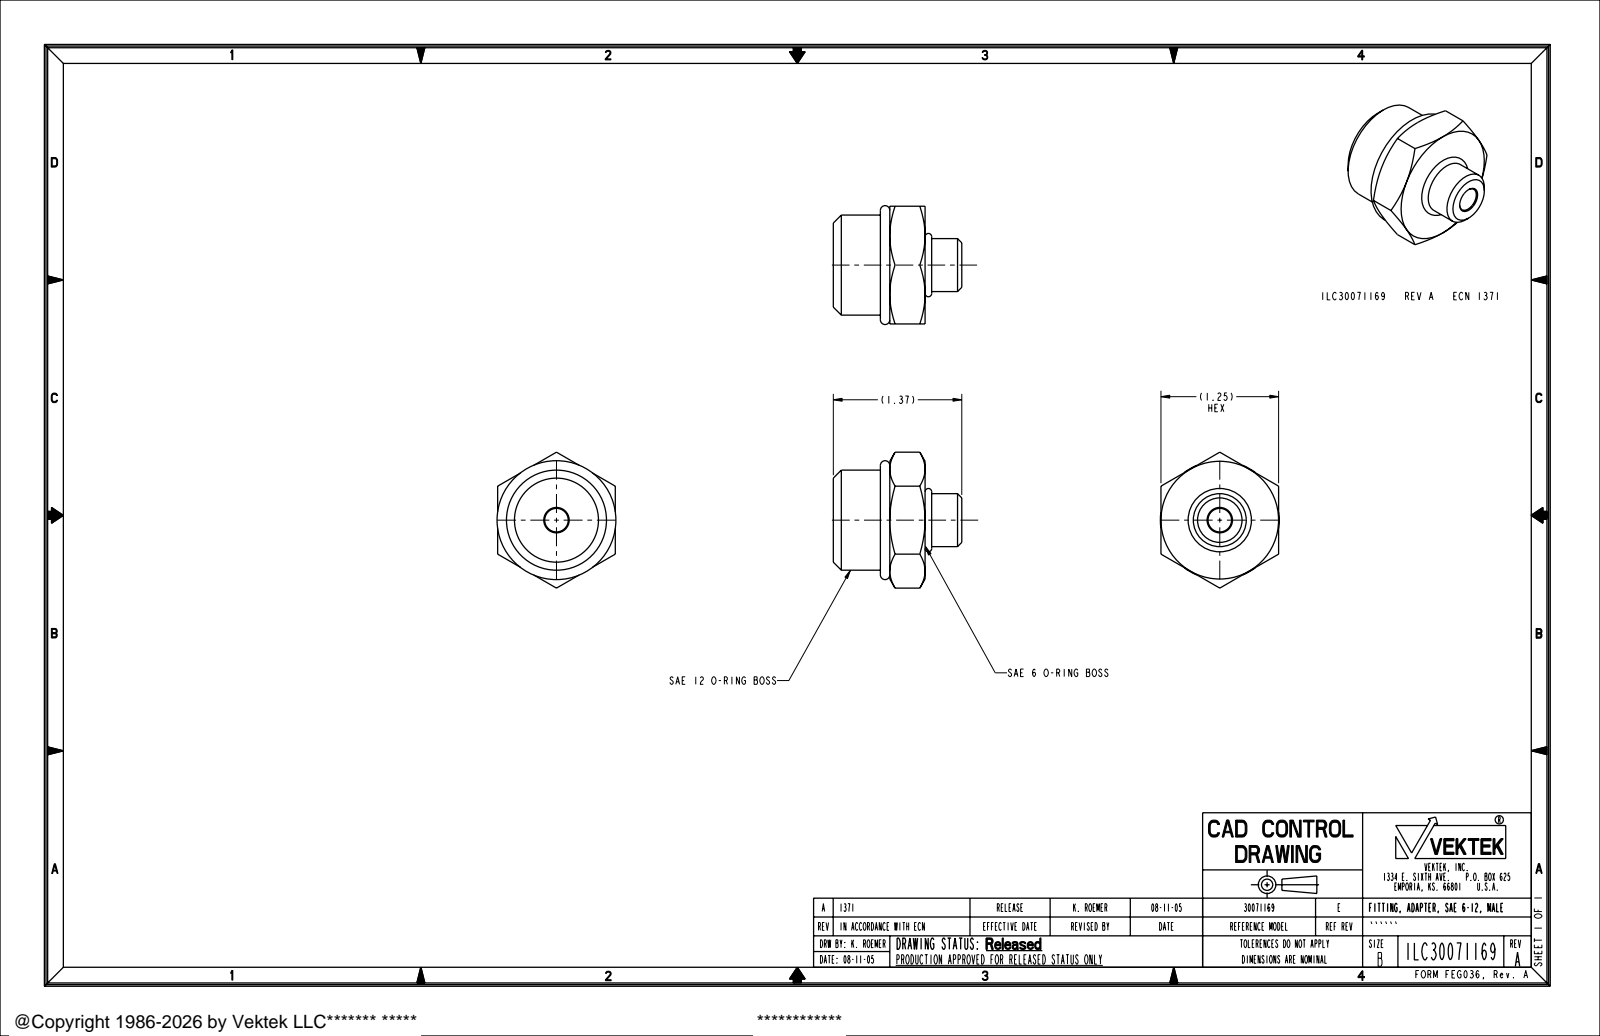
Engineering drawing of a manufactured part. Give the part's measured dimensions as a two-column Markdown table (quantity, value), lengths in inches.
| quantity | value |
| --- | --- |
| part name | ILC30071169 |
| STEP written by | PRO/ENGINEER BY PARAMETRIC TECHNOLOGY CORPORATION, 2004290 (AUTOMOTIVE_DESIGN_CC2) |
| units | inches |
| bodies | 1 solid, 45 faces (10 planar, 9 cylindrical, 26 other) |
| overall size | 1.443 × 1.365 × 1.263 |
| volume | 1.087 in³ |
| surface area | 8.982 in² |
| round holes (diameter × count) | 0.25 × 1 |
| round bosses / shafts (diameter × count) | 1.063 × 1, 0.563 × 1 |
| main face-to-face distances | 0.975, 1.25, 0.6, 0.375, 1.25, 1.365, 0.765, 0.39 |
